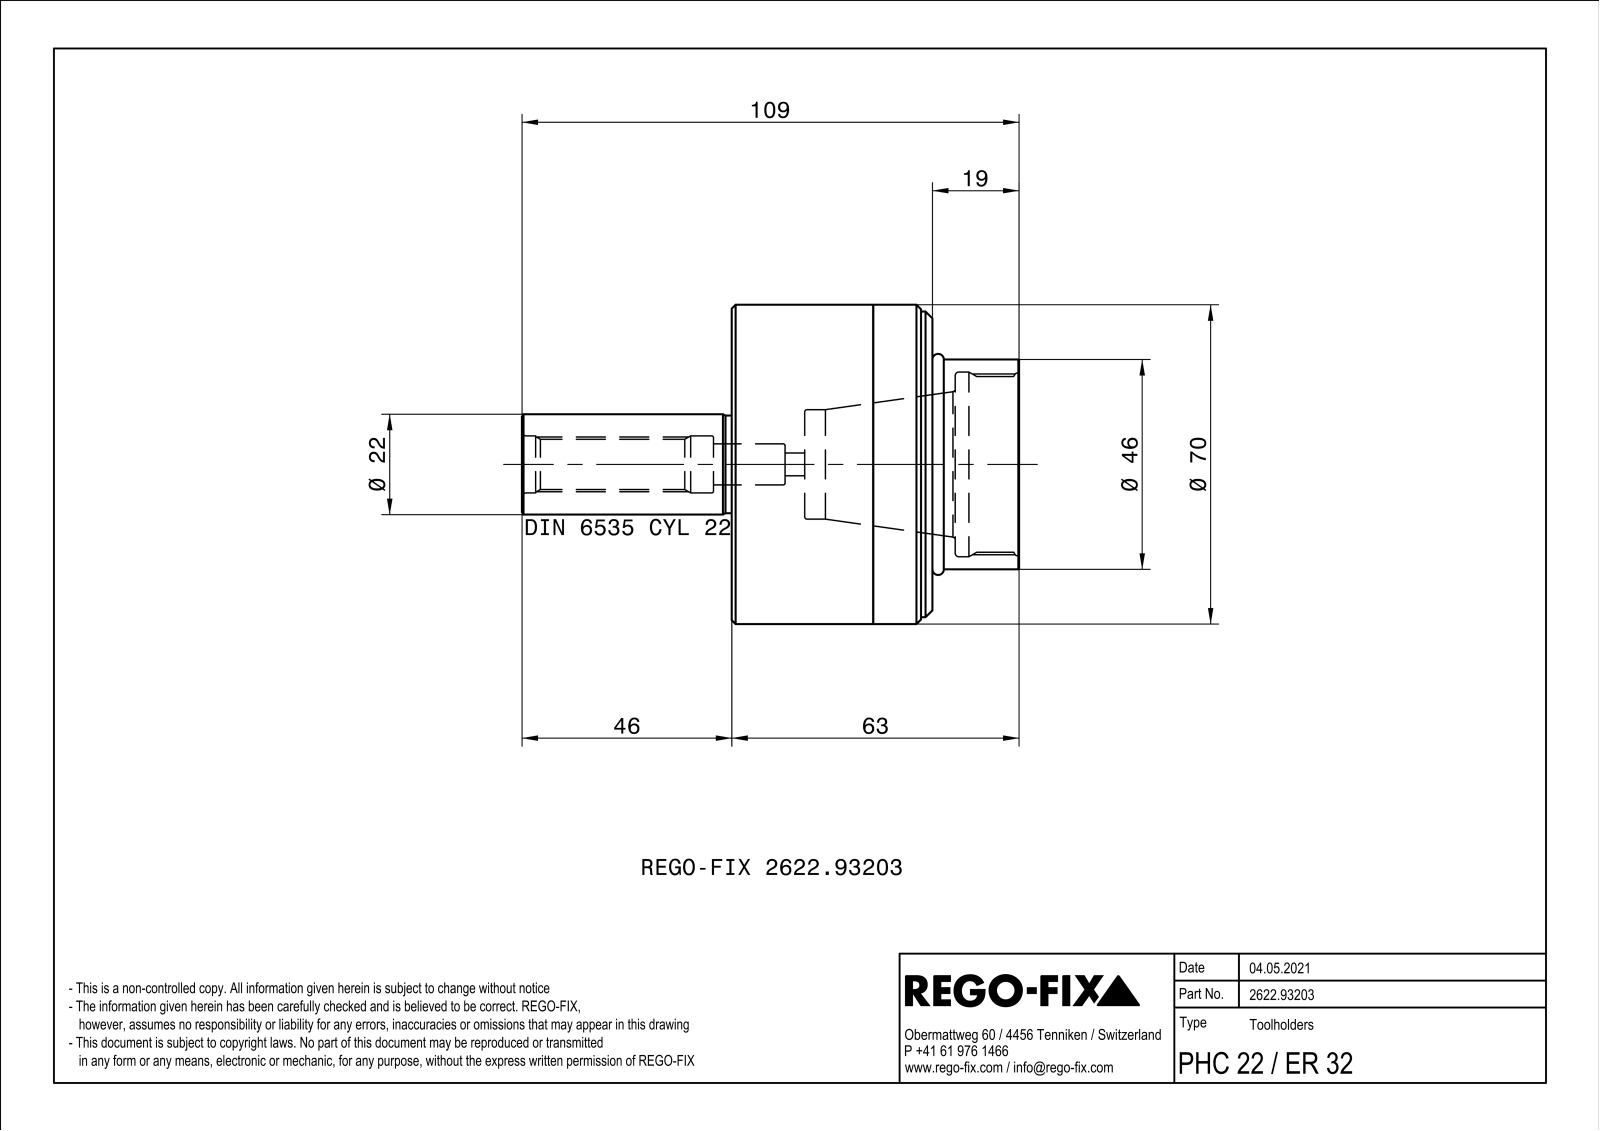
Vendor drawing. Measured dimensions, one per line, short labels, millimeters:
name: NOCUT
written by: SIEMENS PLM Software Solid Edge ST10 (AUTOMOTIVE_DESIGN)
unit: mm
bodies: 1 solid, 128 faces (27 planar, 37 cylindrical, 64 other)
size: 109 × 70 × 70
volume: 138 511 mm³; area: 52 855 mm²
holes: 4× ⌀5, 1× ⌀2.11, 1× ⌀3.2, 1× ⌀5.2, 1× ⌀7.4, 1× ⌀9, 1× ⌀11, 1× ⌀12.5, 1× ⌀24, 1× ⌀38.5, 1× ⌀40.5, 1× ⌀46
bosses: 1× ⌀70, 1× ⌀67, 1× ⌀60, 1× ⌀58.5, 1× ⌀58.4, 1× ⌀54, 1× ⌀53.4, 1× ⌀36
face distances: 6, 12, 5.7, 12.3, 6.3, 26, 18, 32, 44, 38.3
hole spacings: 24, 33.94, 48, 27.8
